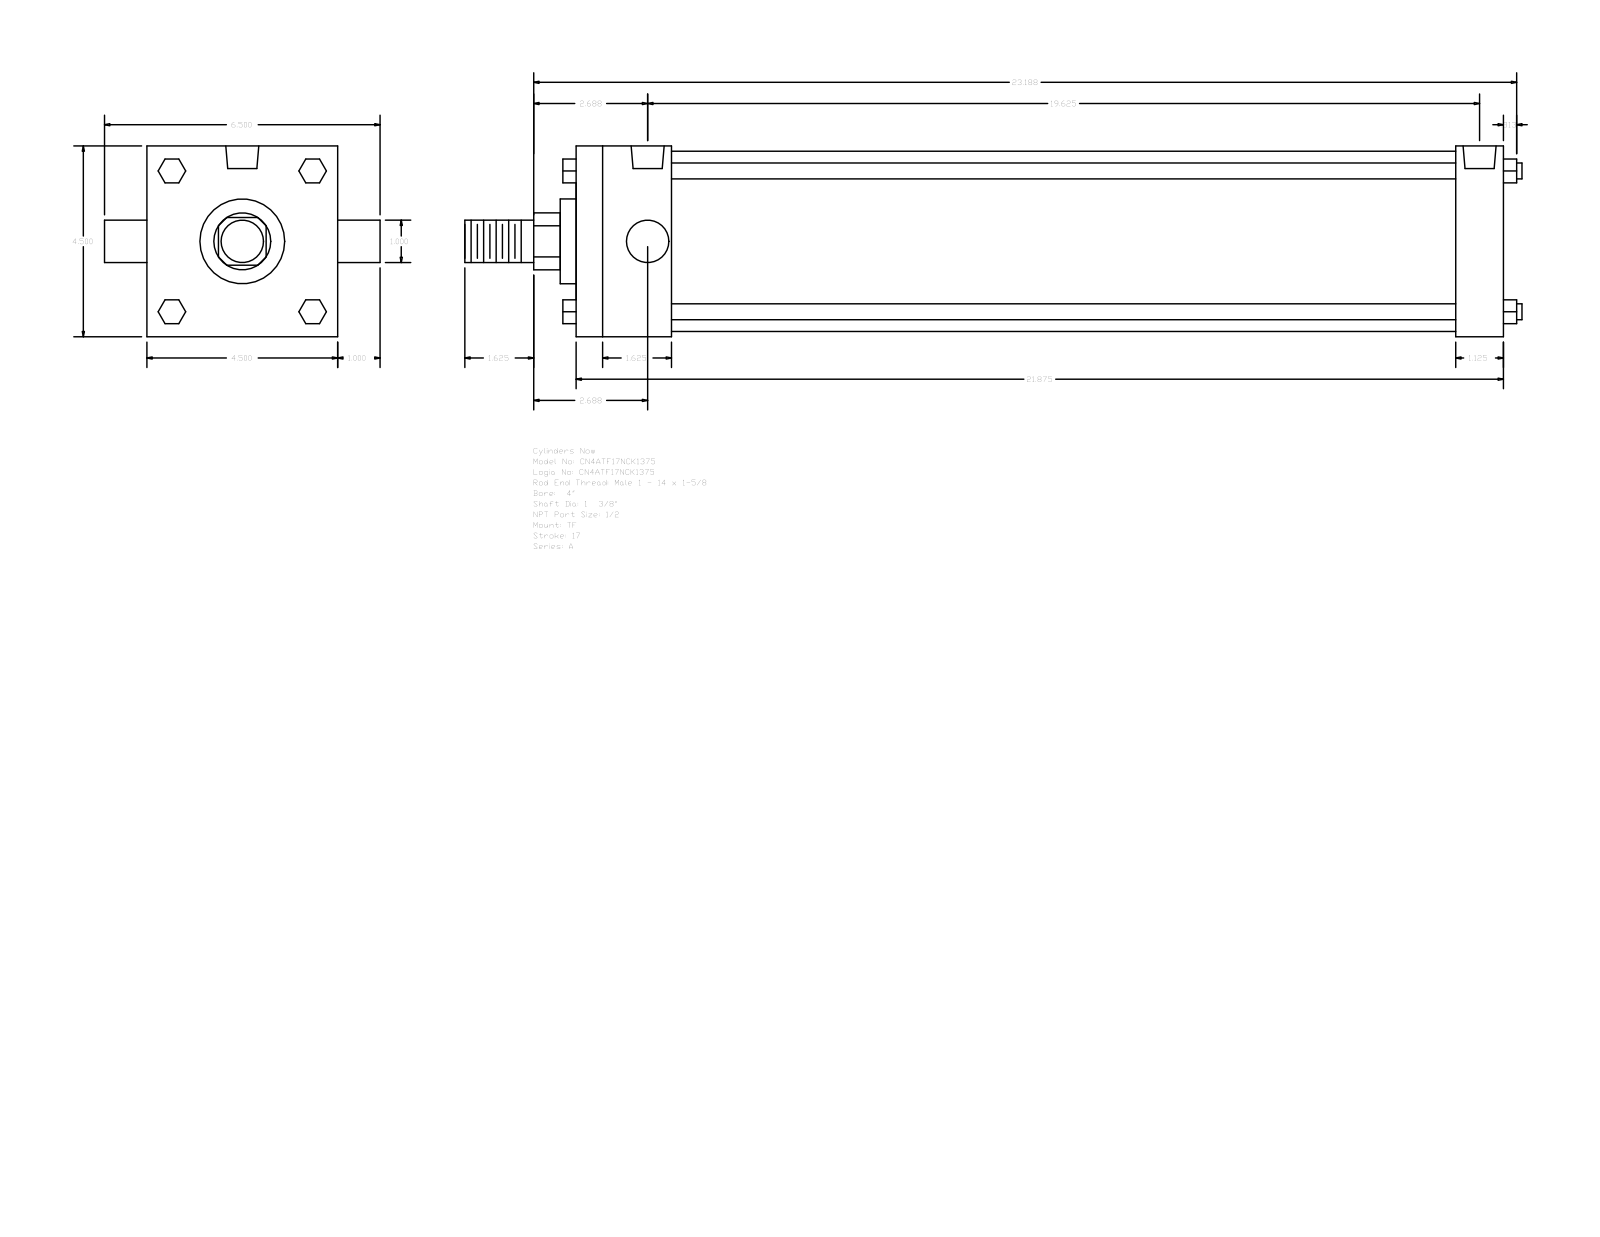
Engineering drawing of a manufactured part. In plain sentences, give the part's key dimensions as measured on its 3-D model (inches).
The part is named "A_TF__0400_1.375". Its 3-D file was written by "GSSL Pune (CONFIG_CONTROL_DESIGN)". It is 0 solids with 120 faces: 92 planar, 28 cylindrical and 0 other. Overall it measures 24.937 by 6.5 by 4.5 inches. Round holes: 3 of diameter 0.344, 2 of diameter 0.778. Round bosses or shafts: 4 of diameter 0.375, 2 of diameter 1, 1 of diameter 4.25, 1 of diameter 2, 1 of diameter 1.375. Partial cylindrical surfaces (rounded edges, fillets, slot ends): 1 of radius 0.672. The main face-to-face distances are 4.5, 21.875, 2.25, 20.75, 1.125, 18.5, 19.625, 2.625, 0.563, 1. The hole center spacings are 0.125, 19.5, 19.375, 19.625.
